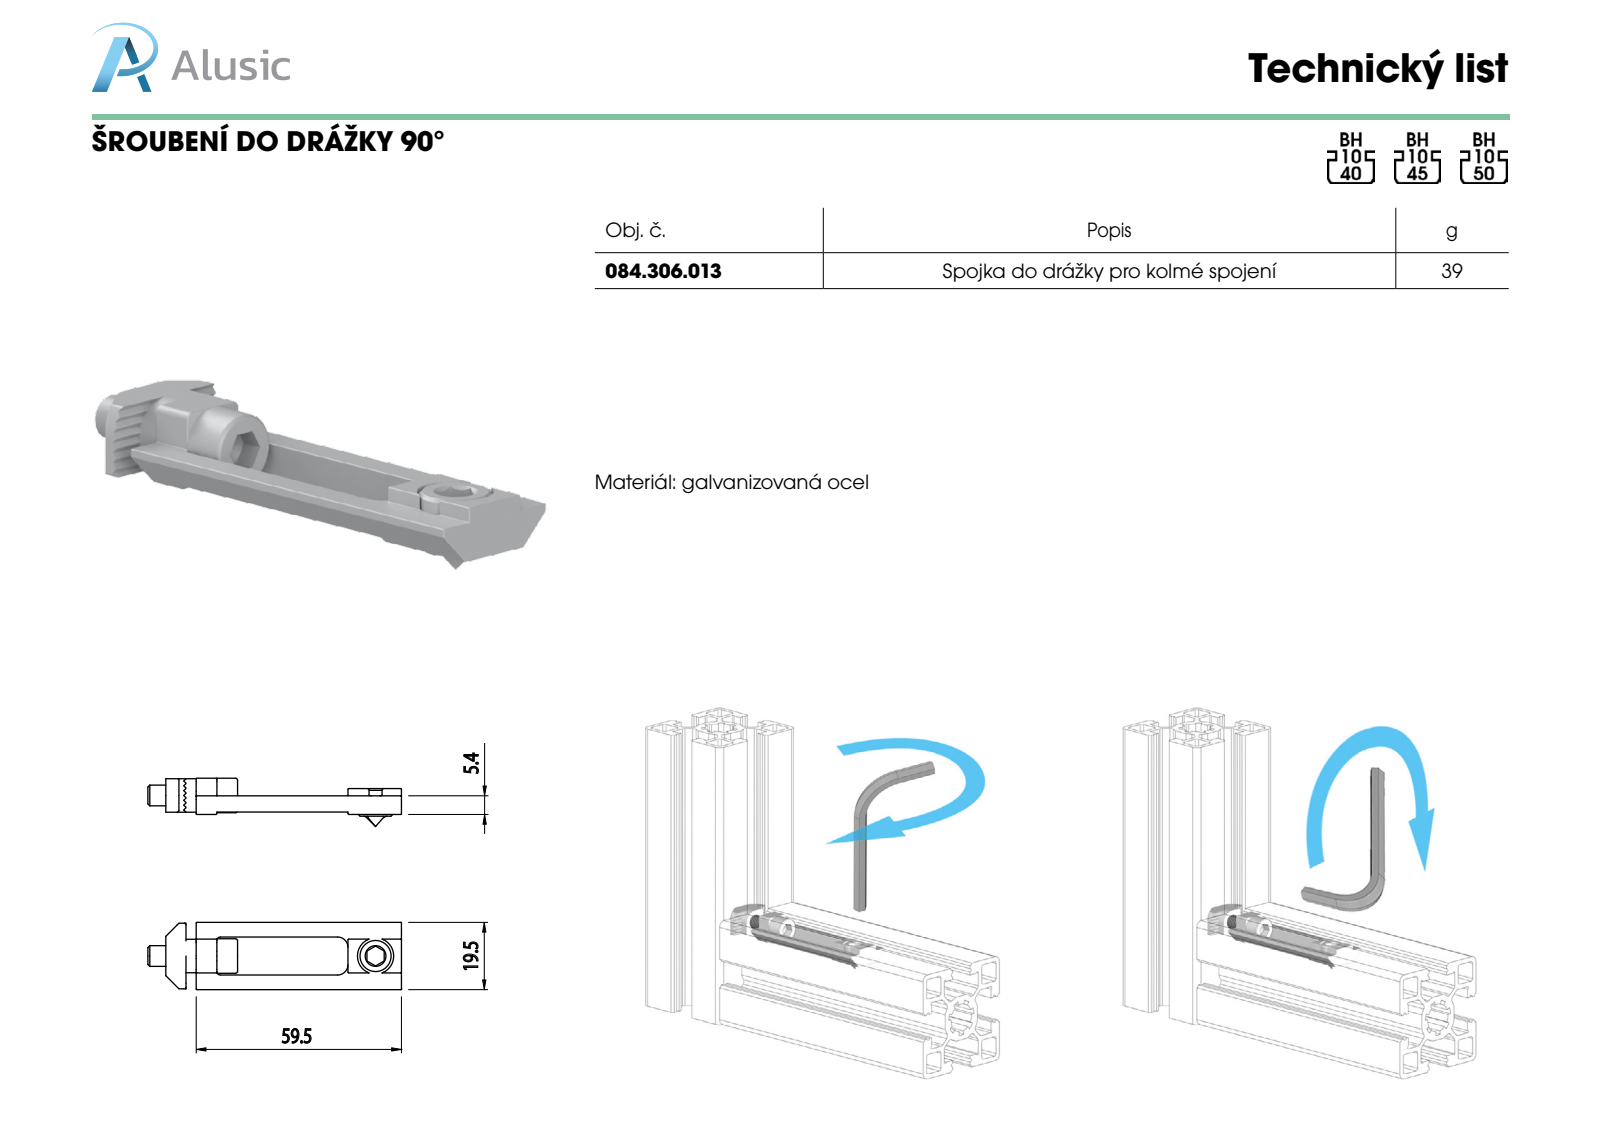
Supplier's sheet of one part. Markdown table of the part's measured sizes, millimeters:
| quantity | value |
| --- | --- |
| part name | 099d1045m-01_Fertigteil; Zylinderschraube-DIN912-M6x18_Standard; 084.306.013; 096h10430_096 h 10 6 30 s04 (+1 more) |
| STEP written by | SolidWorks 2011 (CONFIG_CONTROL_DESIGN) |
| units | millimeters |
| bodies | 4 solids, 242 faces (97 planar, 94 cylindrical, 51 other) |
| overall size | 73.5 × 19.5 × 14 |
| volume | 5 255 mm³ |
| surface area | 4 887 mm² |
| round holes (diameter × count) | 5 × 2, 6.5 × 1, 9 × 1, 10.5 × 1 |
| round bosses / shafts (diameter × count) | 10 × 2, 6 × 1 |
| partial cylindrical surfaces (radius × count) | 0.2 × 39, 0.5 × 6, 1 × 5, 0.3 × 2, 3 × 2, 4.85 × 1, 9.5 × 1 |
| main face-to-face distances | 11, 5.4, 6, 10.35, 0.65, 4.95, 9.7, 4.25, 15.25, 59.5 |
